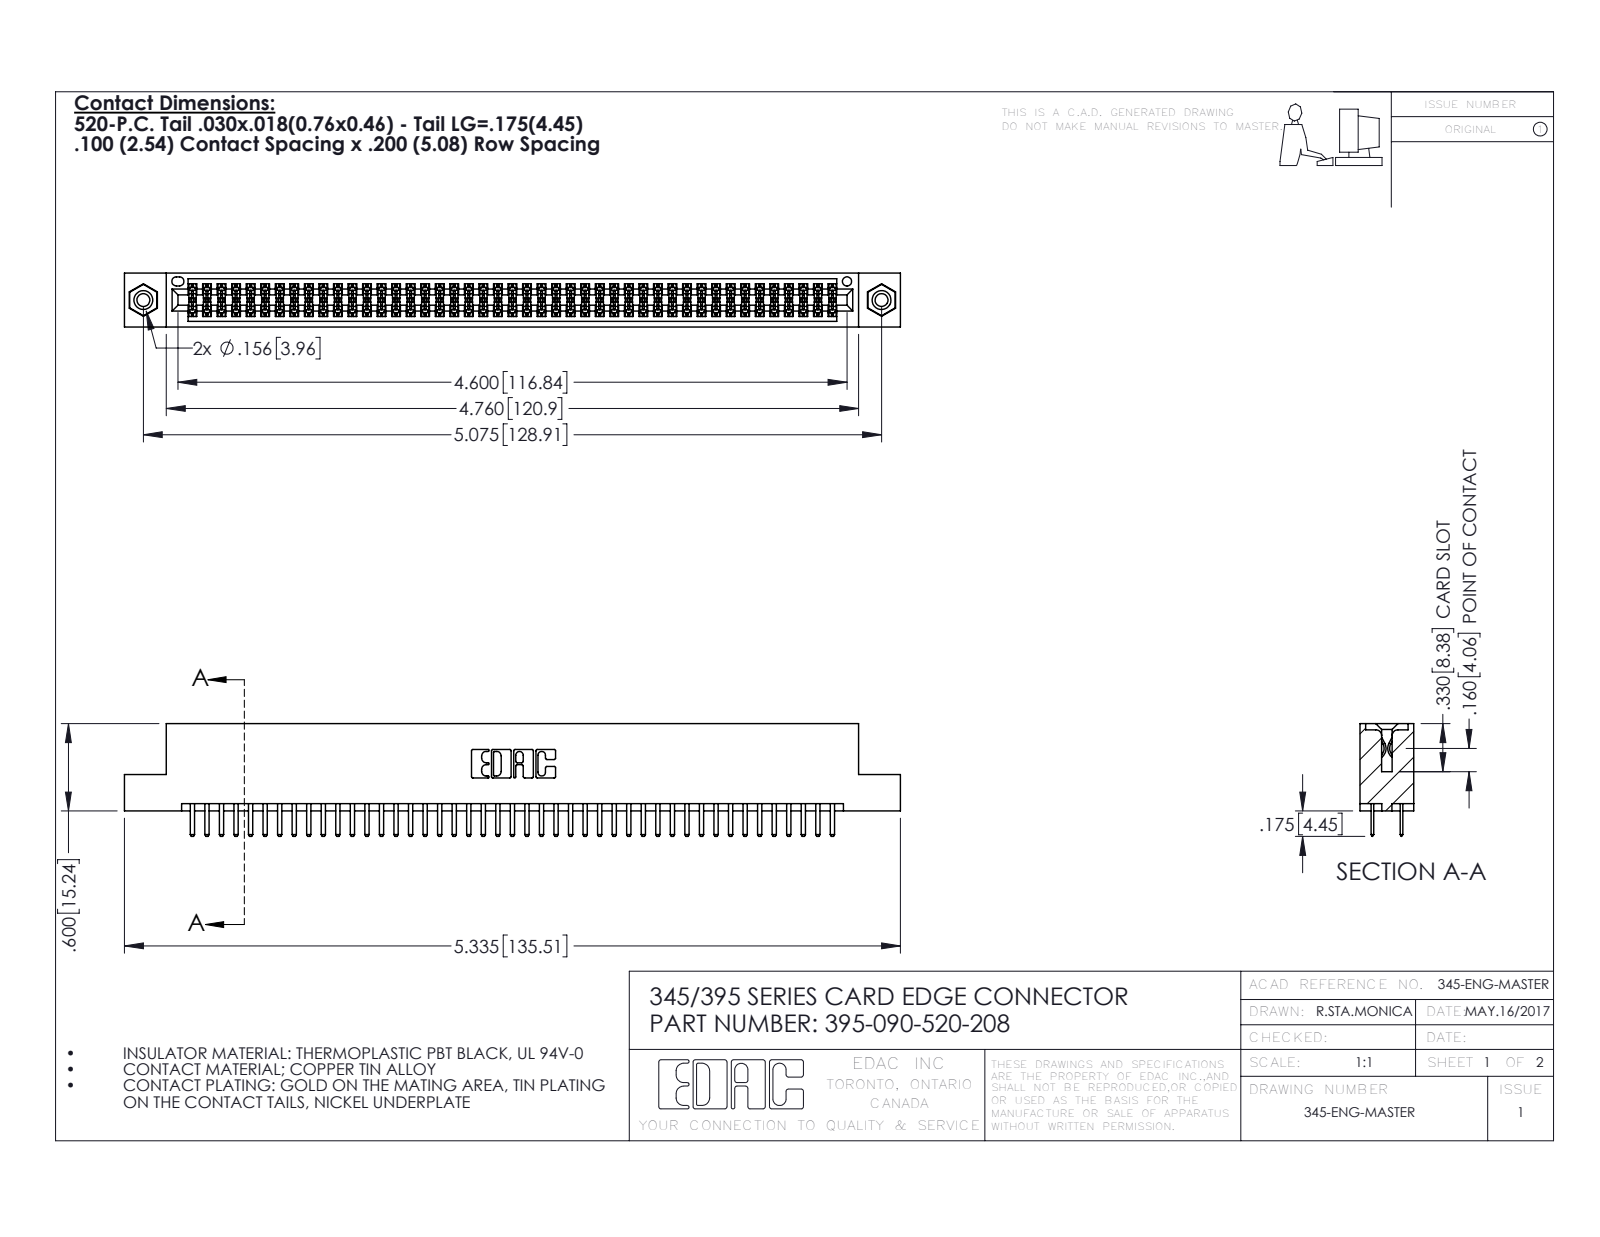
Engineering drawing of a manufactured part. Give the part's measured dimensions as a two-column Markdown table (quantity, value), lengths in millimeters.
| quantity | value |
| --- | --- |
| part name | 395-090-520-208; 345-292-001_345-293-120; 345-250-001_345-250-003-102; 345 Part_Flush Mounting Lugs - 0.156 Dia-TI |
| STEP written by | SolidWorks 2016 (CONFIG_CONTROL_DESIGN) |
| units | millimeters |
| bodies | 93 solids, 5046 faces (3262 planar, 1768 cylindrical, 16 other) |
| overall size | 135.5 × 19.7 × 9.4 |
| volume | 13 100 mm³ |
| surface area | 19 420 mm² |
| round holes (diameter × count) | 2.3 × 2, 3.2 × 2, 4 × 2, 1.6 × 1 |
| round bosses / shafts (diameter × count) | 3.9 × 2 |
| partial cylindrical surfaces (radius × count) | 0.2 × 135, 0.3 × 94, 0.3 × 22, 0.2 × 6, 0.8 × 6, 0.7 × 3, 0.4 × 2, 0.5 × 2 |
| main face-to-face distances | 1.8, 7.6, 5.1, 9.4, 2.5, 6.9, 0.6, 5.7, 0.6, 1.8 |
| hole center spacings | 6.9, 122.9, 128.9 |
